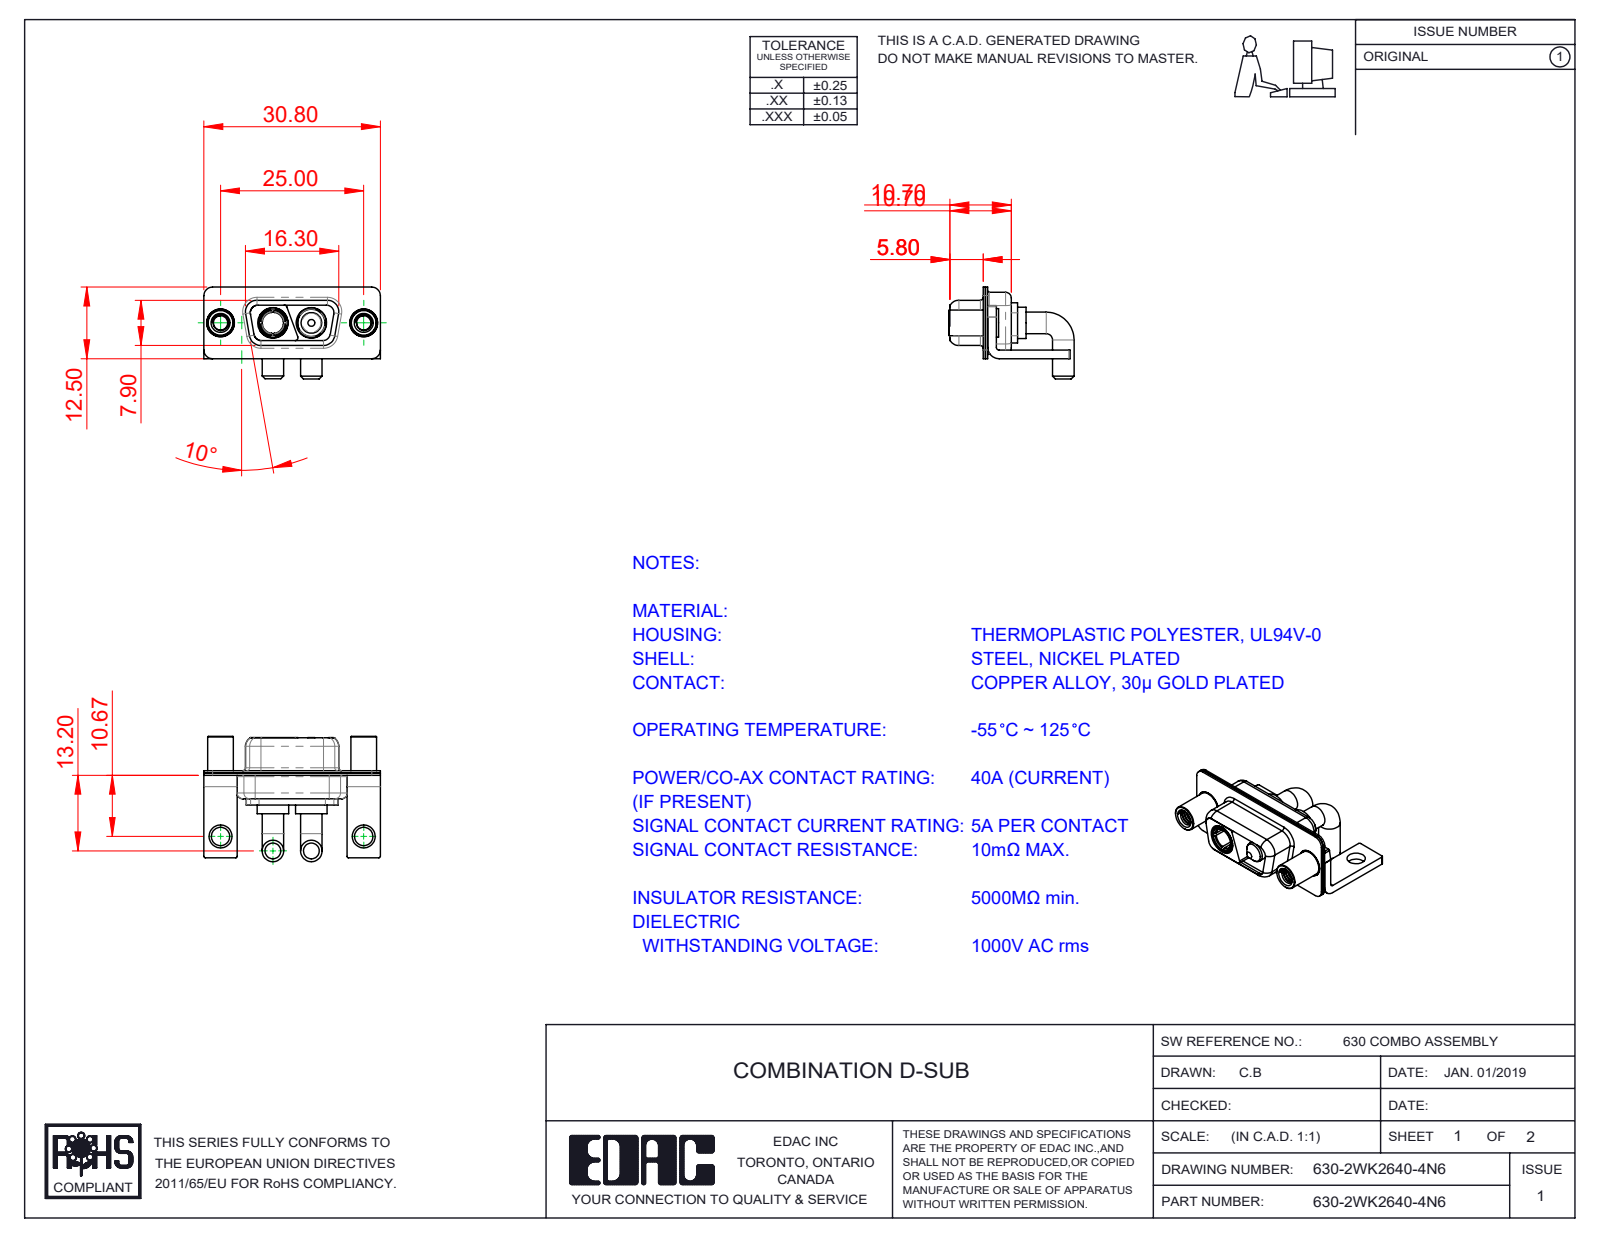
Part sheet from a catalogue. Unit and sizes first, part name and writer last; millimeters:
Units: millimetres
Overall size (bounding box): 30.8 × 21.88 × 16.05
Round holes (diameter × count): ⌀4.85 ×4, ⌀2.5 ×2, ⌀3.2 ×2, ⌀4 ×2, ⌀4.05 ×2, ⌀5.3 ×2, ⌀3.7 ×1
Round bosses / shafts (diameter × count): ⌀3.75 ×4, ⌀5.5 ×2, ⌀5.2 ×2, ⌀5 ×2, ⌀4.95 ×2, ⌀4.8 ×2, ⌀4.75 ×2, ⌀4.5 ×2
Partial cylindrical surfaces — rounded edges, fillets, slot ends (radius × count): R0.25 ×16, R1.5 ×16, R2 ×13, R1.35 ×8, R1.6 ×8, R0.5 ×7, R0.6 ×4, R0.65 ×4
Main face-to-face distances: 0.4, 1.5, 0.8, 1.4, 8.45, 0.45, 1.8, 8.9, 2.3, 3.7
Hole centre spacings: 9.14, 15.86, 25, 6.72
Volume: 2 227 mm³ · Surface area: 5 114 mm²
Bodies: 11 solids, 499 faces (128 planar, 256 cylindrical, 115 other)
Part name (STEP PRODUCT): Power Pin_40A RA; 630Combo Shell Front_09 Contacts; 630Combo Threaded Standoff_D; 630Combo Shell Rear_09 Contacts (+4 more)
STEP written by: SolidWorks 2020 (CONFIG_CONTROL_DESIGN)
